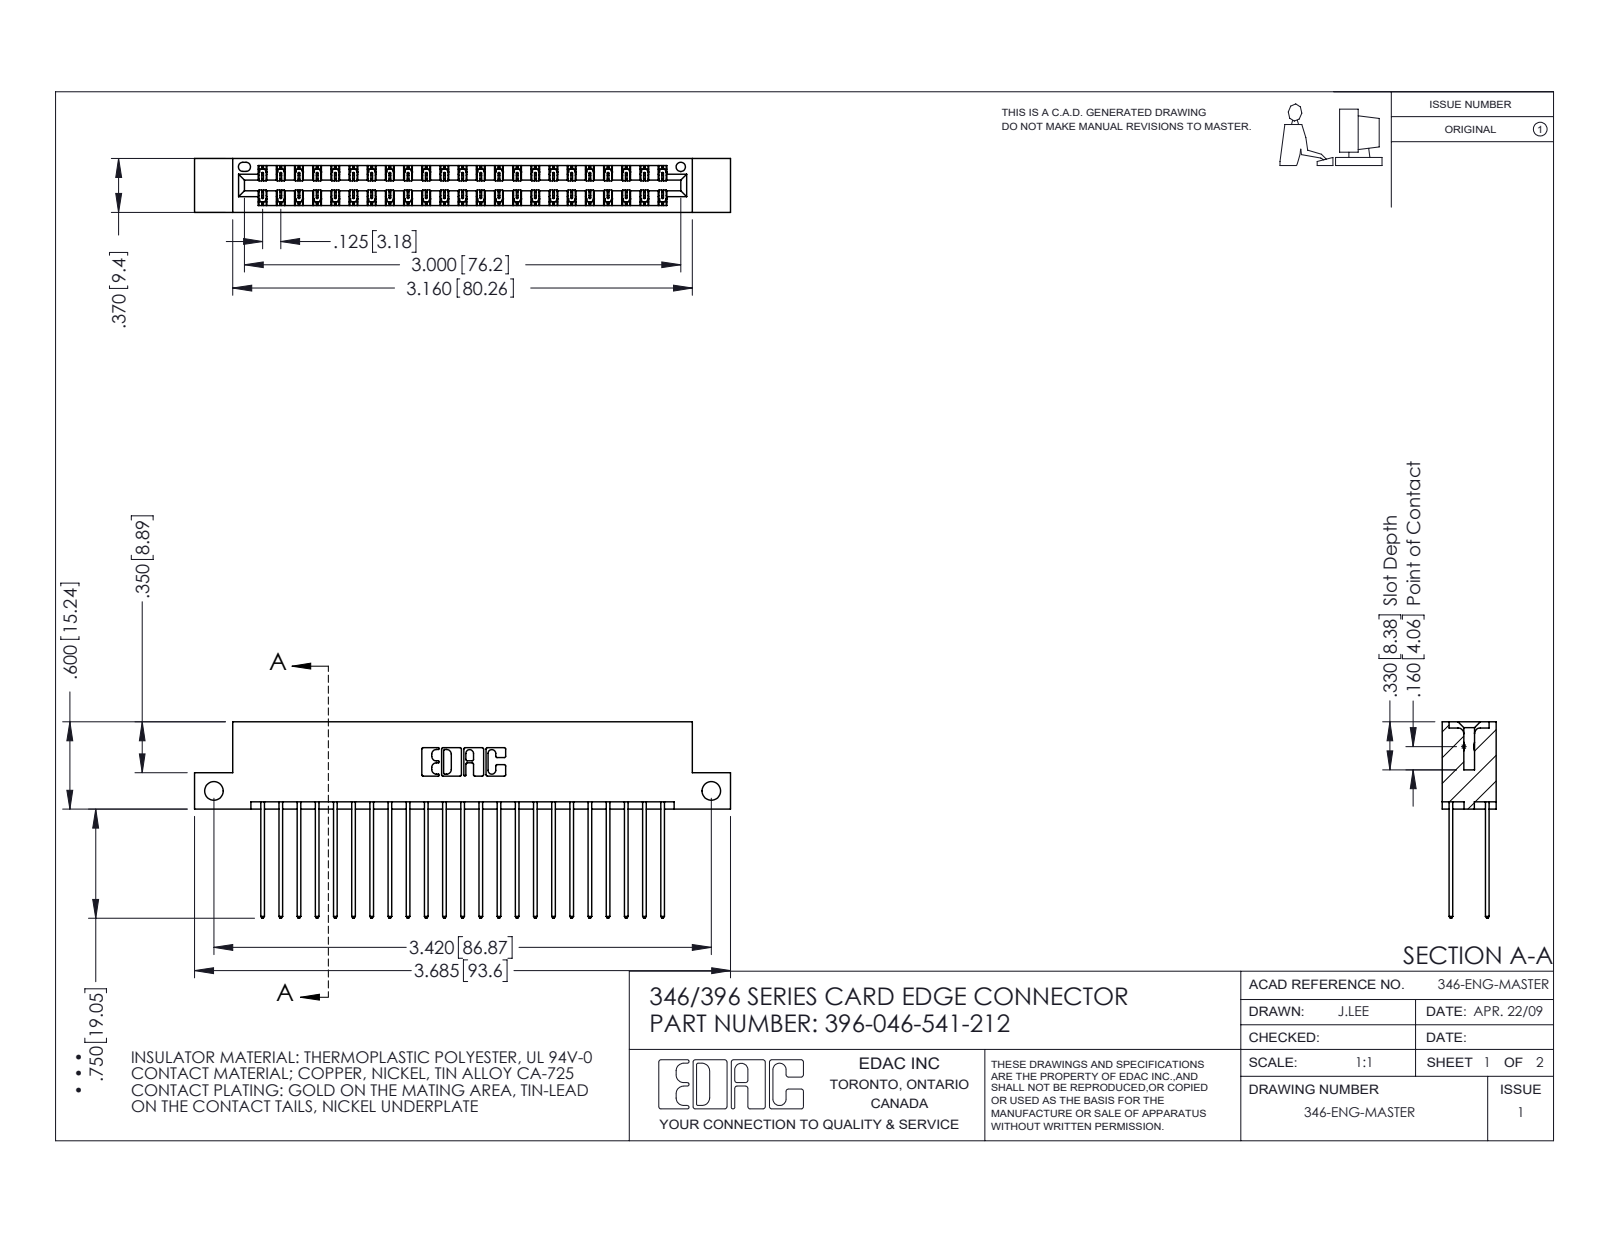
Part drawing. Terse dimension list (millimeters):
name: 346 Part_Flush Mounting Lugs - Side Mount; 345-292-001_345-293-141; 396-046-541-212
written by: SolidWorks 2016 (CONFIG_CONTROL_DESIGN)
unit: mm
bodies: 47 solids, 2514 faces (1686 planar, 828 cylindrical, 0 other)
size: 93.6 × 34.3 × 9.4
volume: 9 160 mm³; area: 13 410 mm²
holes: 2× ⌀3.3, 1× ⌀1.6
rounds: 69× R0.2, 46× R0.3, 22× R0.3, 6× R0.2, 6× R0.8, 3× R0.7, 2× R0.4, 2× R0.6
face distances: 1.2, 8.2, 6.4, 1.8, 7.6, 0.6, 9.4, 7, 3.8, 5.6
hole spacings: 86.9
